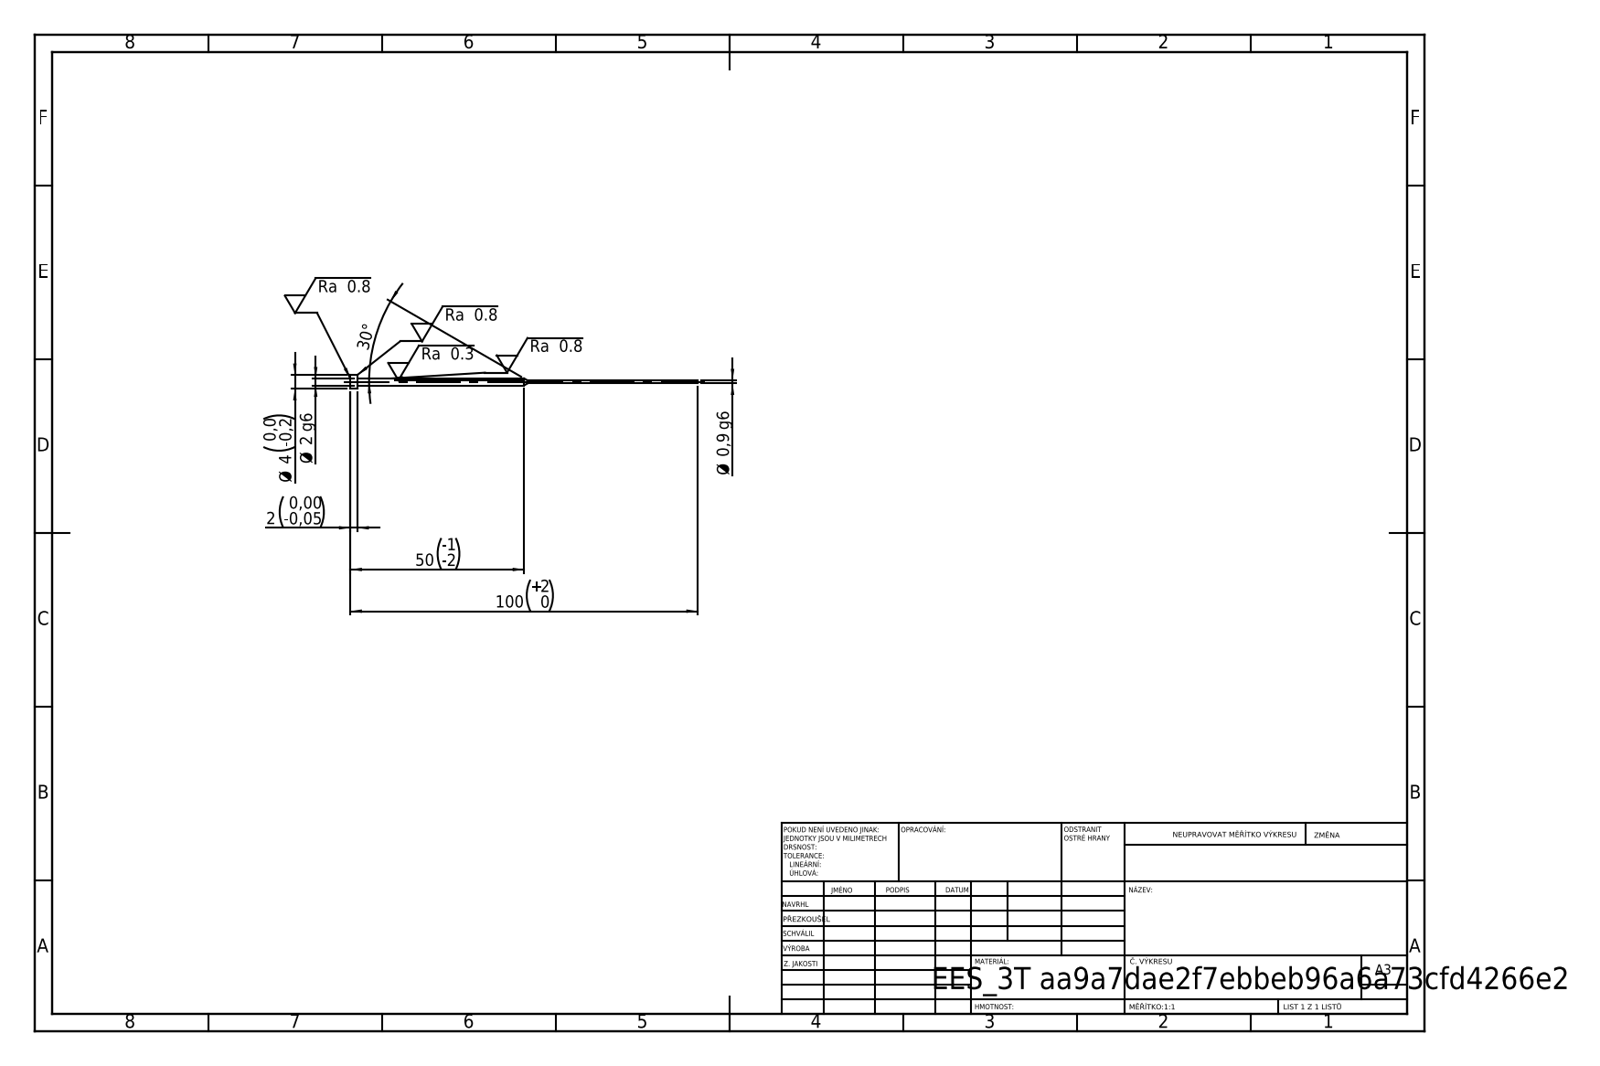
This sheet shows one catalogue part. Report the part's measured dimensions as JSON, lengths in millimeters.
{"step_written_by": "SolidWorks 2019 (CONFIG_CONTROL_DESIGN)", "units": "millimeters", "bodies": {"solids": 1, "faces": 11, "planar": 3, "cylindrical": 6, "other": 2}, "overall_size": [100, 4, 4], "volume_mm3": 209, "surface_area_mm2": 493, "round_bosses_or_shafts": [[4, 1], [2, 1], [0.9, 1]], "face_to_face_distances": [2, 98, 100]}
